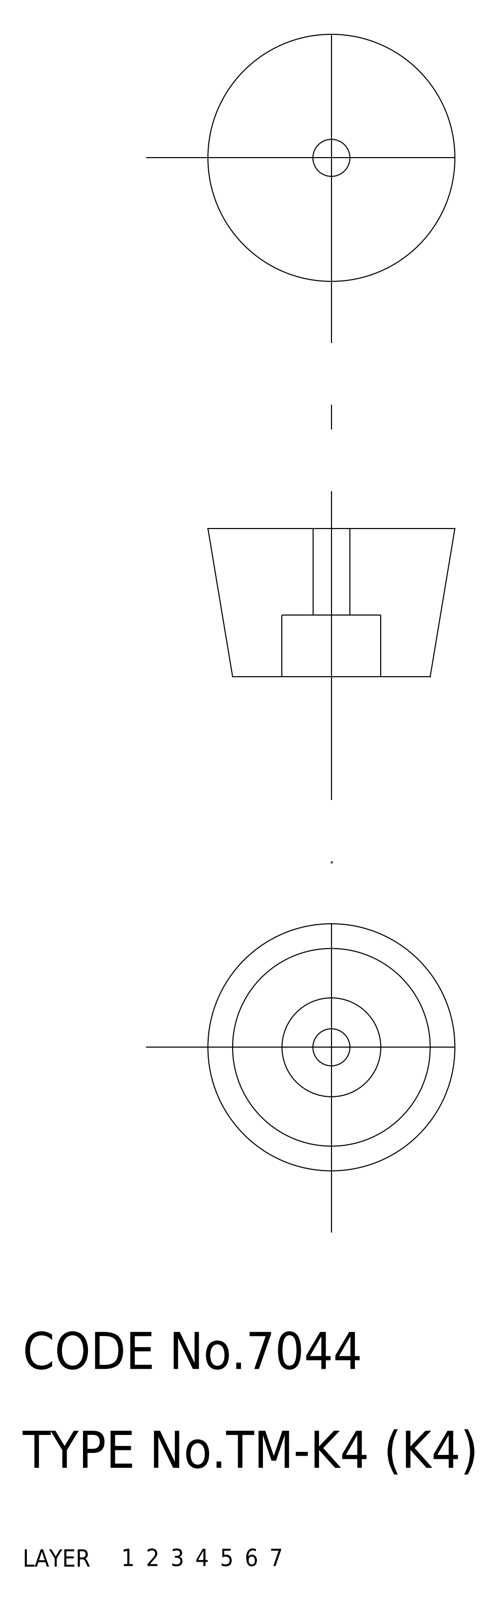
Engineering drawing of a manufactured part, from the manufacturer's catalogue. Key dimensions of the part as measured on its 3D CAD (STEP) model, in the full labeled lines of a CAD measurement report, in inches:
Part name (STEP PRODUCT): rubber foot
STEP written by: CADfix (AUTOMOTIVE_DESIGN)
Units: inches
Bodies: 1 solid, 9 faces (0 planar, 0 cylindrical, 9 other)
Overall size (bounding box): 0.787 × 0.787 × 0.472
Volume: 0.169 in³ · Surface area: 2.142 in²
